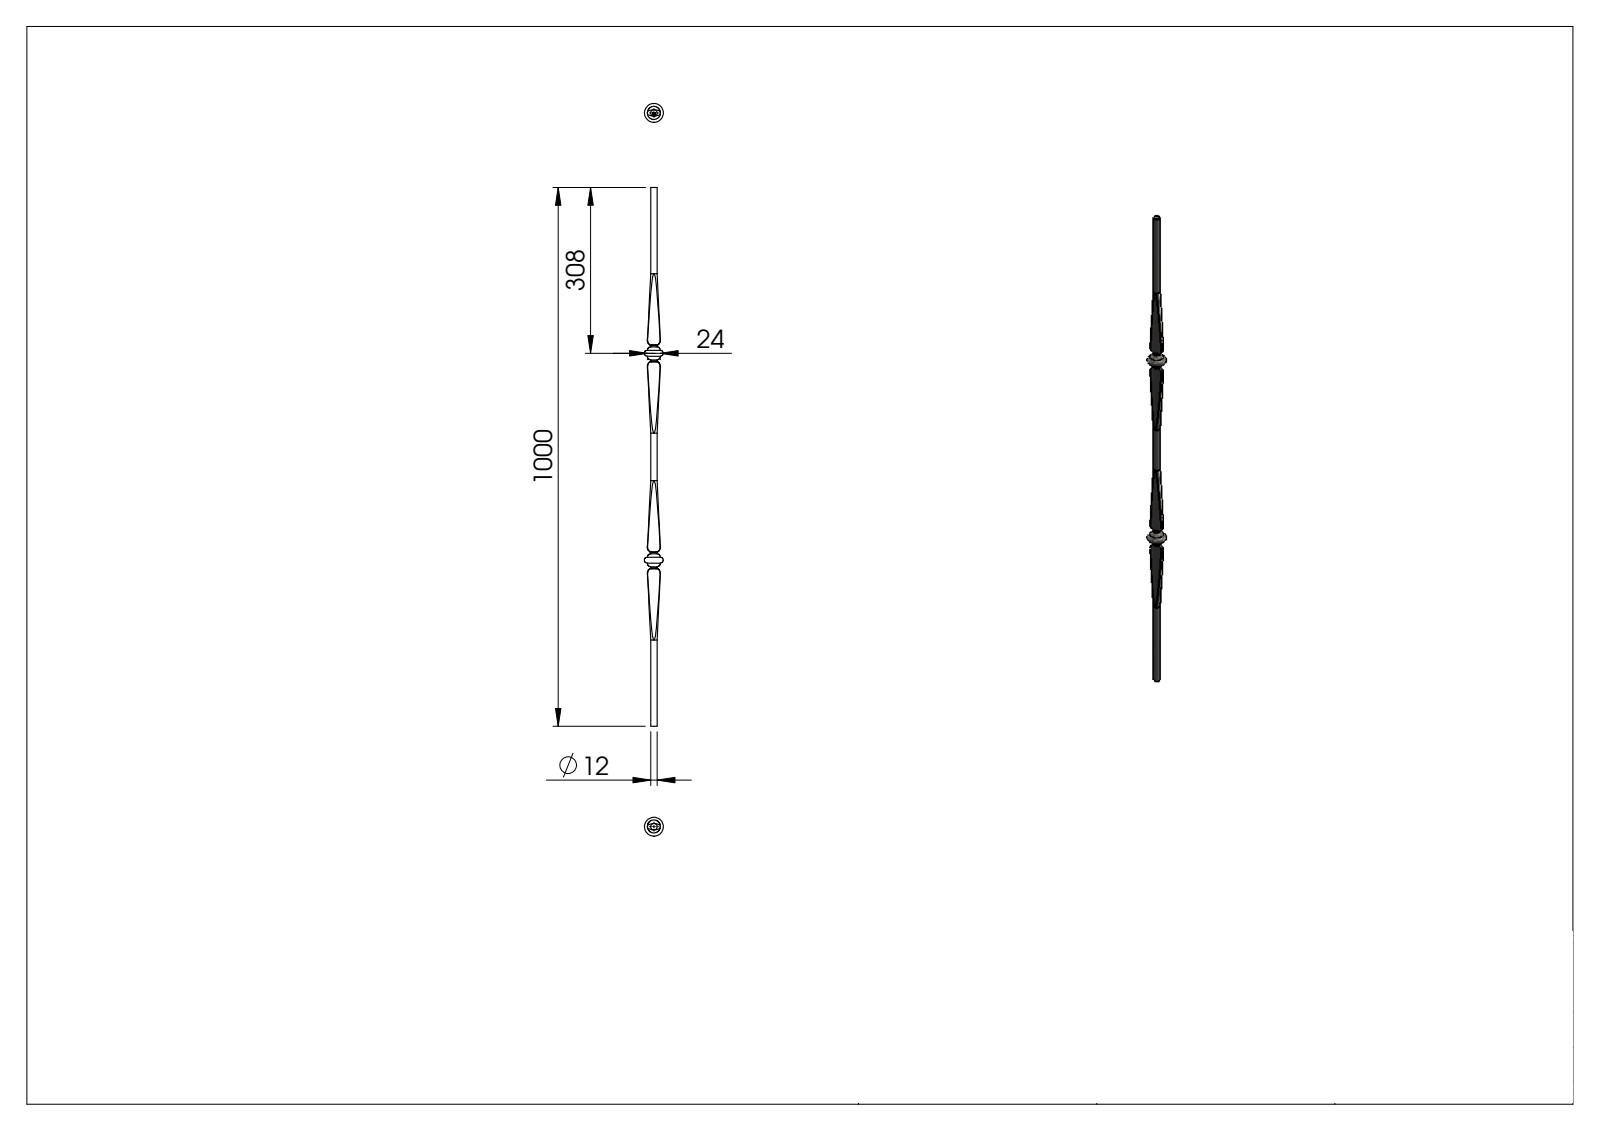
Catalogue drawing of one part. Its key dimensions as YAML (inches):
part_name: "56109-240"
step_written_by: "SolidWorks 2015 (CONFIG_CONTROL_DESIGN)"
units: inches
bodies: {solids: 1, faces: 332, planar: 130, cylindrical: 14, other: 188}
overall_size: [39.37, 1.378, 1.378]
volume: 9.002
surface_area: 75.38
round_bosses_or_shafts:
  - {diameter: 0.472, count: 1}
face_to_face_distances: [39.37, 11.535, 12.717, 26.654, 27.835, 1.181, 15.118, 16.299, 13.937, 0.02]
